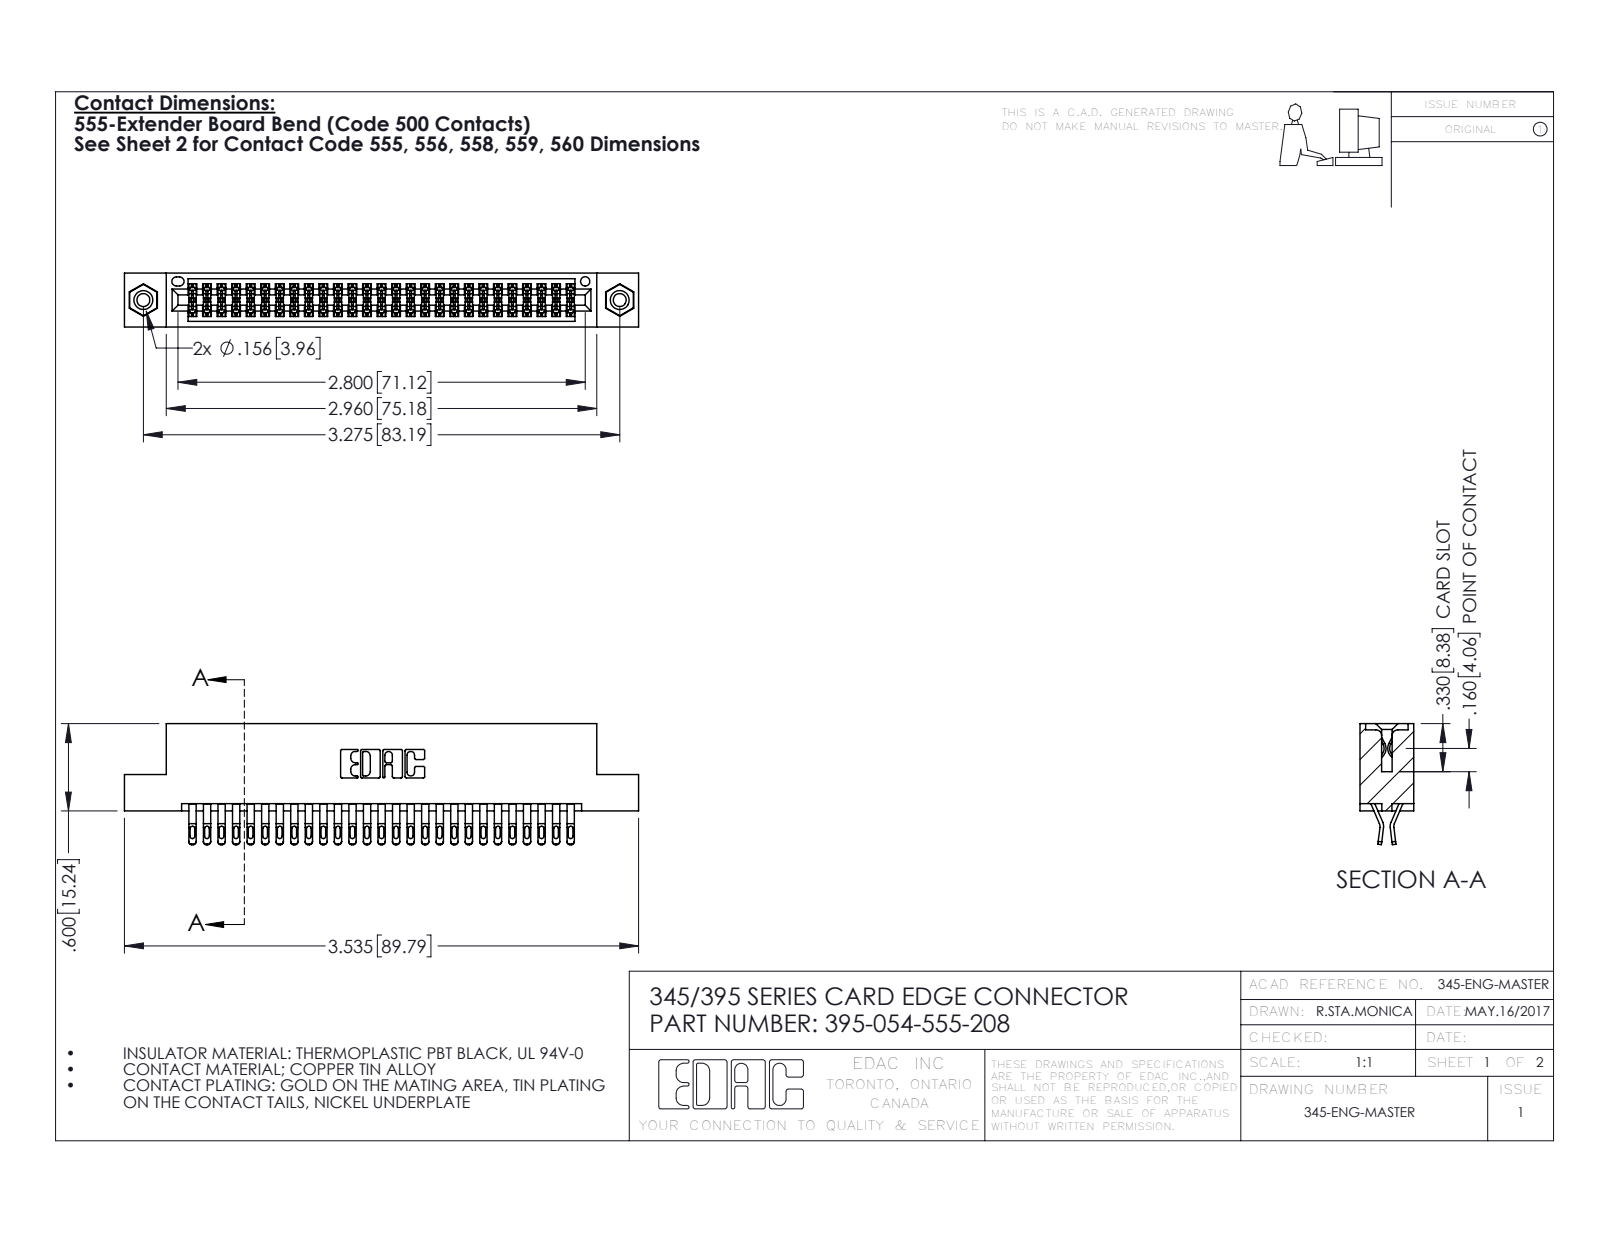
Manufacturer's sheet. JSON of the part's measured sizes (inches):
{"part_name": "345 Part_Flush Mounting Lugs - 0.156 Dia-TI; 395-054-555-208; 345-292-001_555 Tail; 345-250-001_345-250-003-102", "step_written_by": "SolidWorks 2016 (CONFIG_CONTROL_DESIGN)", "units": "inches", "bodies": {"solids": 57, "faces": 3210, "planar": 1786, "cylindrical": 1408, "other": 16}, "overall_size": [3.535, 0.832, 0.37], "volume_in3": 0.533, "surface_area_in2": 20.42, "round_holes": [[0.089, 2], [0.125, 2], [0.156, 2], [0.064, 1]], "round_bosses_or_shafts": [[0.155, 2]], "partial_cylinders_radius": [[0.016, 135], [0.02, 108], [0.006, 81], [0.01, 22], [0.007, 6], [0.031, 6], [0.026, 3], [0.01, 2]], "face_to_face_distances": [0.072, 0.298, 0.2, 0.37, 0.025, 0.098, 0.272, 0.225, 0.175, 0.149], "hole_center_spacings": [0.27, 3.04, 3.275]}
